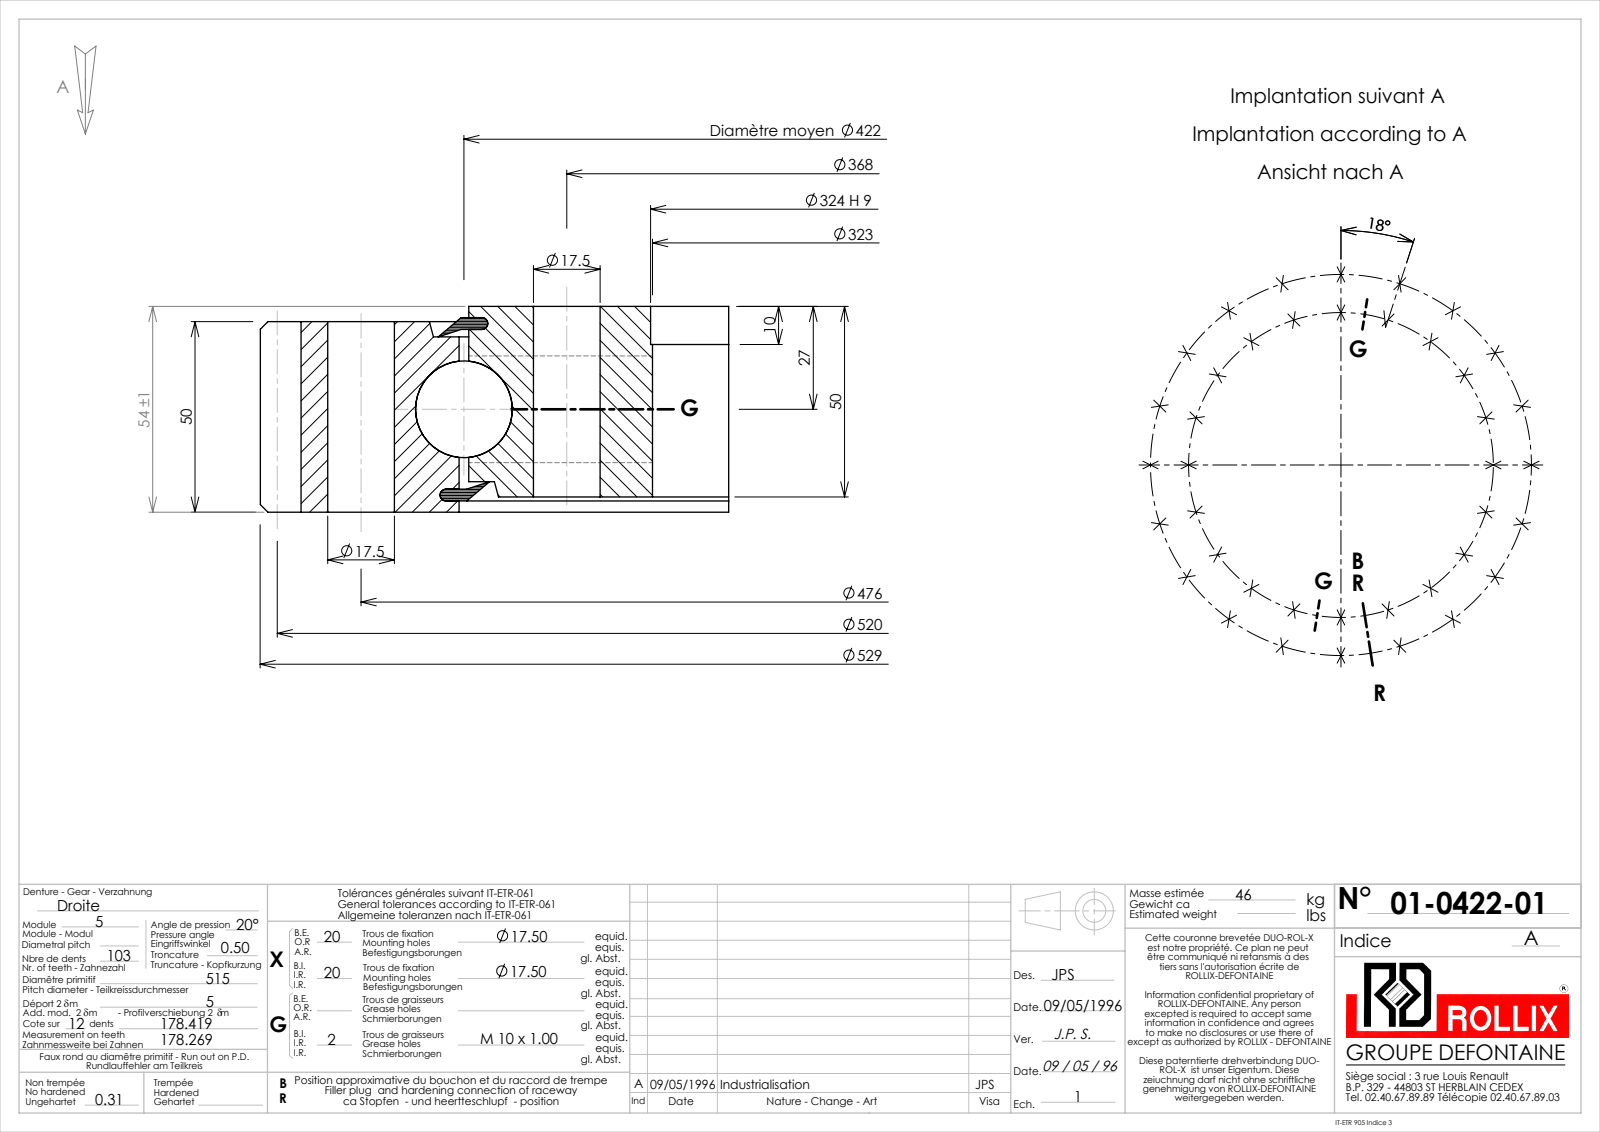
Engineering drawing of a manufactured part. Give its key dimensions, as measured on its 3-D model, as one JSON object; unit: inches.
{"part_name": "01-0422-01", "step_written_by": "SolidWorks 2016 (CONFIG_CONTROL_DESIGN)", "units": "inches", "bodies": {"solids": 5, "faces": 767, "planar": 221, "cylindrical": 307, "other": 239}, "overall_size": [20.826, 20.824, 2.126], "volume_in3": 318.1, "surface_area_in2": 1272, "round_holes": [[0.689, 40], [0.354, 2], [12.717, 1], [12.756, 1], [16.714, 1]], "round_bosses_or_shafts": [[16.514, 1]], "partial_cylinders_radius": [[9.99, 1], [10.413, 1]], "face_to_face_distances": [0.157, 1.969, 1.811, 2.126, 0.116, 2.01, 0.041, 1.852, 0.238, 1.888], "hole_center_spacings": [9.37, 13.251, 16.698, 18.509, 11.844, 14.835, 16.413, 5.791]}
